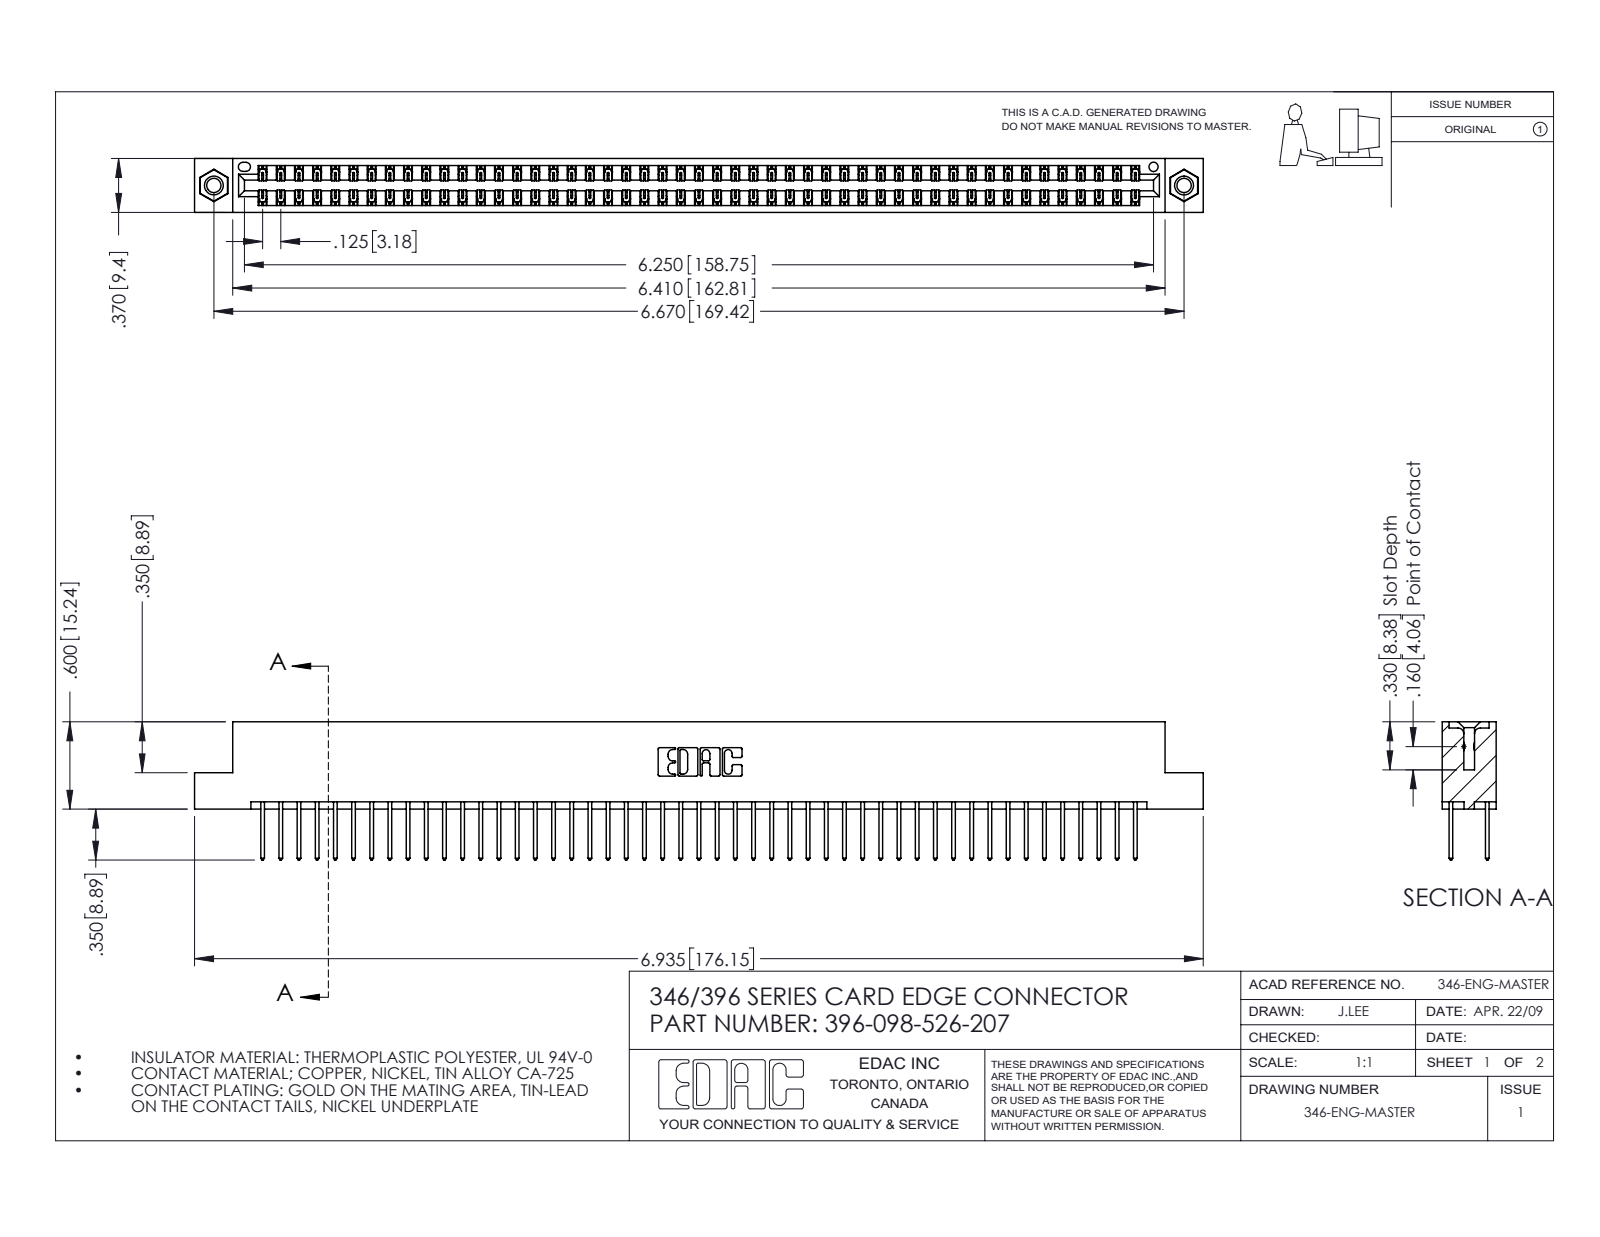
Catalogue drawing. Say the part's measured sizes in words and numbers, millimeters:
The part is named "345-250-001_345-250-005-103; 346 Part_Flush Mounting Lugs - 0.156 Dia-TI; 396-098-526-207; 345-292-001_345-293-126". Its 3-D file was written by "SolidWorks 2016 (CONFIG_CONTROL_DESIGN)". It is 101 solids with 5278 faces: 3538 planar, 1724 cylindrical and 16 other. Overall it measures 176.1 by 24.1 by 9.4 millimeters. Its volume is 17 370 cubic millimeters and its surface area 24 750 square millimeters. Round holes: 2 of diameter 2.5, 2 of diameter 3.2, 2 of diameter 4, 1 of diameter 1.6. Round bosses or shafts: 2 of diameter 3.9. Partial cylindrical surfaces (rounded edges, fillets, slot ends): 147 of radius 0.2, 98 of radius 0.3, 22 of radius 0.3, 6 of radius 0.2, 6 of radius 0.8, 3 of radius 0.7, 2 of radius 0.4, 2 of radius 0.6. The main face-to-face distances are 1.2, 8.2, 6.4, 9.4, 1.8, 7.6, 0.6, 7, 3.8, 5.6. The hole center spacings are 6.2, 164.1, 169.4.
